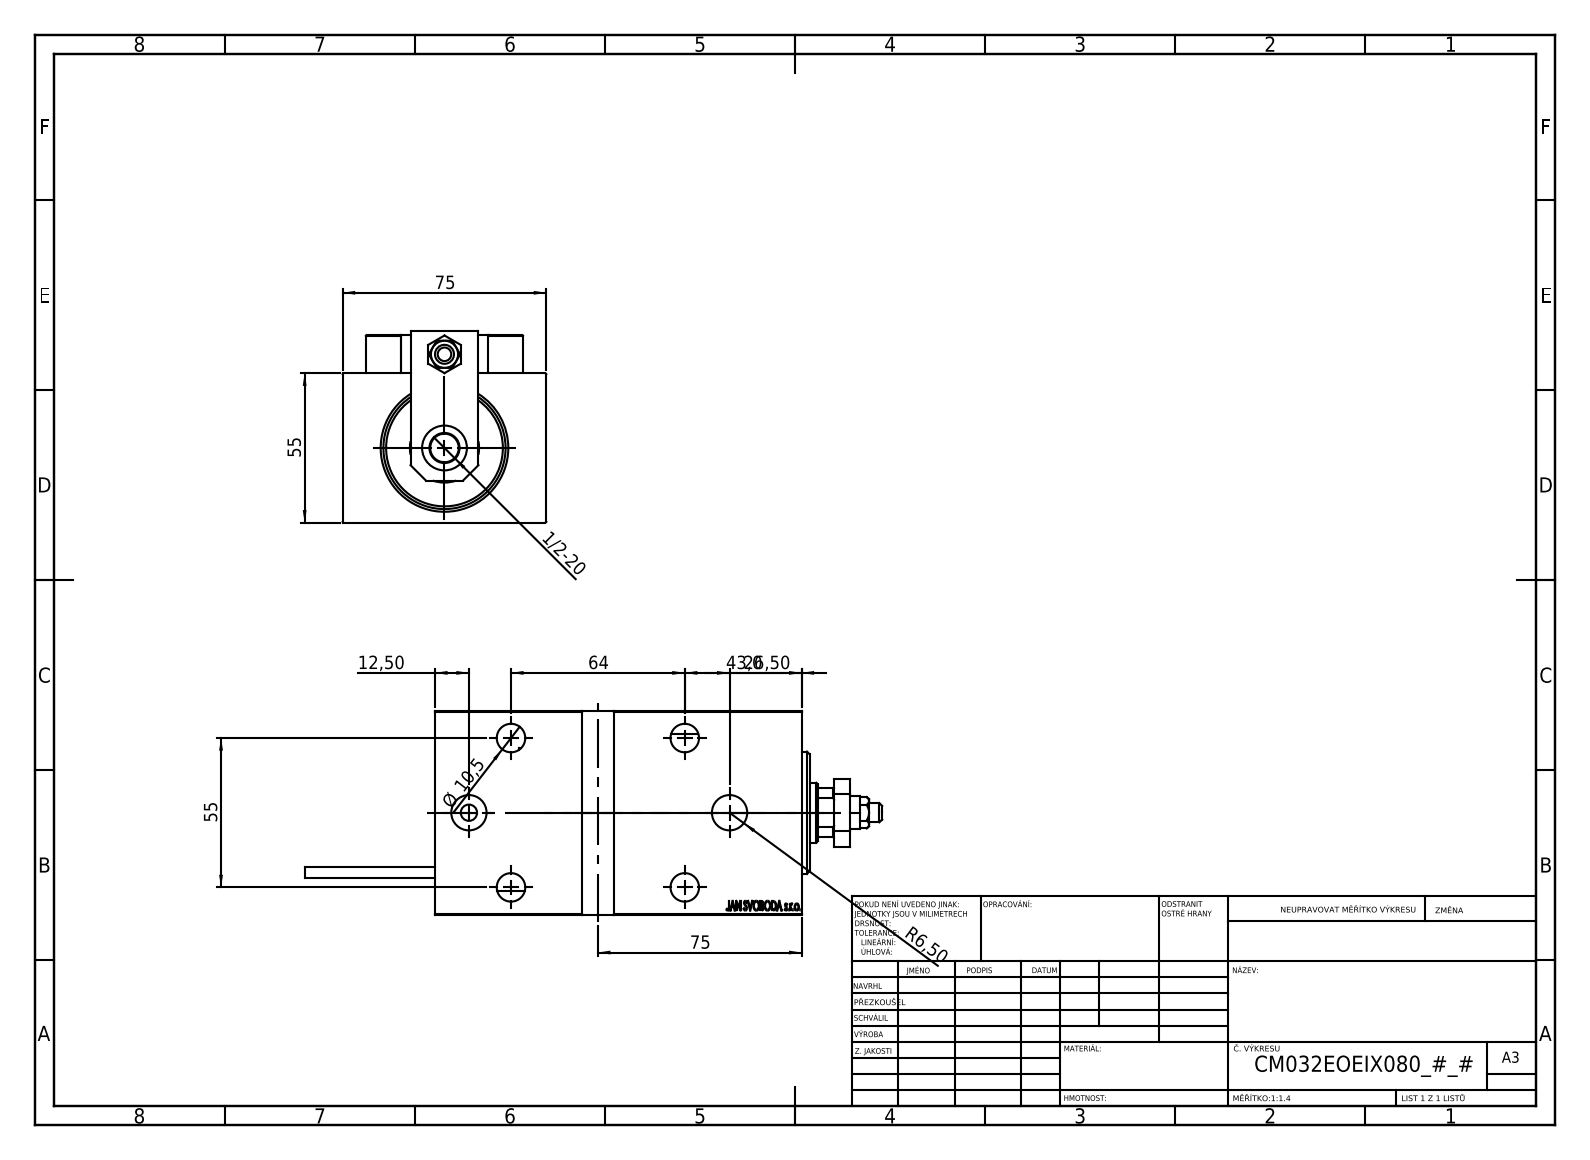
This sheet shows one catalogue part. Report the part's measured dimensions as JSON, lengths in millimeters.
{"part_name": "NUT_D12; SWITCH_X_FRONT_BACK; V450CM_E_Body; ALLEN BOLT D8 (+7 more)", "step_written_by": "SolidWorks 2019 (CONFIG_CONTROL_DESIGN)", "units": "millimeters", "bodies": {"solids": 24, "faces": 1283, "planar": 568, "cylindrical": 174, "other": 541}, "overall_size": [212.7, 75, 70.5], "volume_mm3": 552433, "surface_area_mm2": 108955, "round_holes": [[8, 5], [10.5, 5], [16.5, 5], [3.2, 4], [4, 4], [5, 2], [13, 2], [7, 1], [22, 1], [25.5, 1], [32, 1], [45, 1]], "round_bosses_or_shafts": [[5, 2], [3.8, 2], [34, 1], [13, 1], [11, 1], [6, 1]], "partial_cylinders_radius": [[0.3, 30], [3, 2], [10.5, 1]], "face_to_face_distances": [55, 75, 10, 69, 14, 3, 135, 12, 25, 125], "hole_center_spacings": [11.37, 12.5, 20, 21.91, 28.9, 29.59, 29.69, 31.57]}
